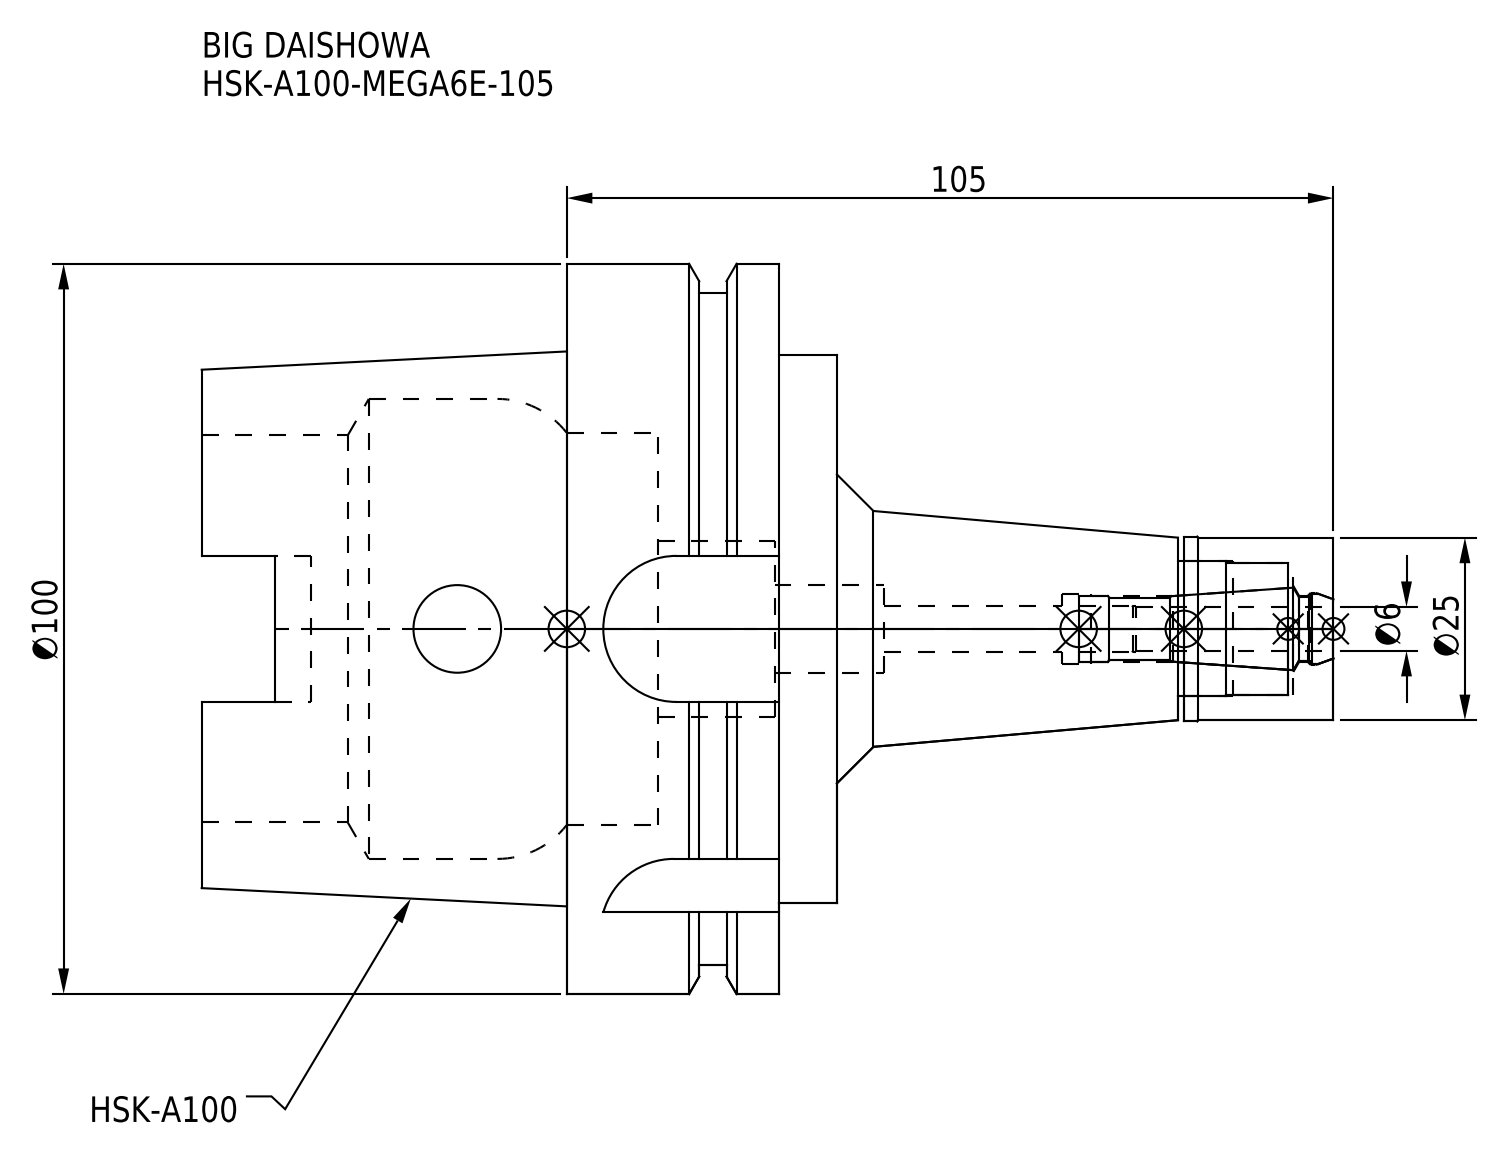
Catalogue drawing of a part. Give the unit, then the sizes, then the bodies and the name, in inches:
Units: inches
Overall size (bounding box): 6.102 × 3.937 × 3.937
Round holes (diameter × count): ⌀0.472 ×2, ⌀0.252 ×1, ⌀0.354 ×1, ⌀0.378 ×1, ⌀0.39 ×1, ⌀0.709 ×1, ⌀0.728 ×1, ⌀0.945 ×1, ⌀2.087 ×1, ⌀2.118 ×1, ⌀2.48 ×1
Round bosses / shafts (diameter × count): ⌀3.937 ×1, ⌀3.622 ×1, ⌀2.953 ×1, ⌀0.996 ×1, ⌀0.984 ×1
Partial cylindrical surfaces — rounded edges, fillets, slot ends (radius × count): R0.192 ×4, R0.394 ×4
Main face-to-face distances: 1.142, 0.315, 1.457, 0.967, 0.652, 0.49, 3.425, 3.11, 2.459, 1.969
Volume: 19.92 in³ · Surface area: 95.87 in²
Bodies: 2 solids, 126 faces (42 planar, 56 cylindrical, 28 other)
Part name (STEP PRODUCT): HA100ME06105-060_ASM.stp; DXF_TEMP_ASSY_ASM_4_ASM.stp; HSK-A100-MEGA6E-105; HSK-A100-MEGA6E-105-060.stp (+3 more)
STEP written by: SolidWorks 2019 (CONFIG_CONTROL_DESIGN)
